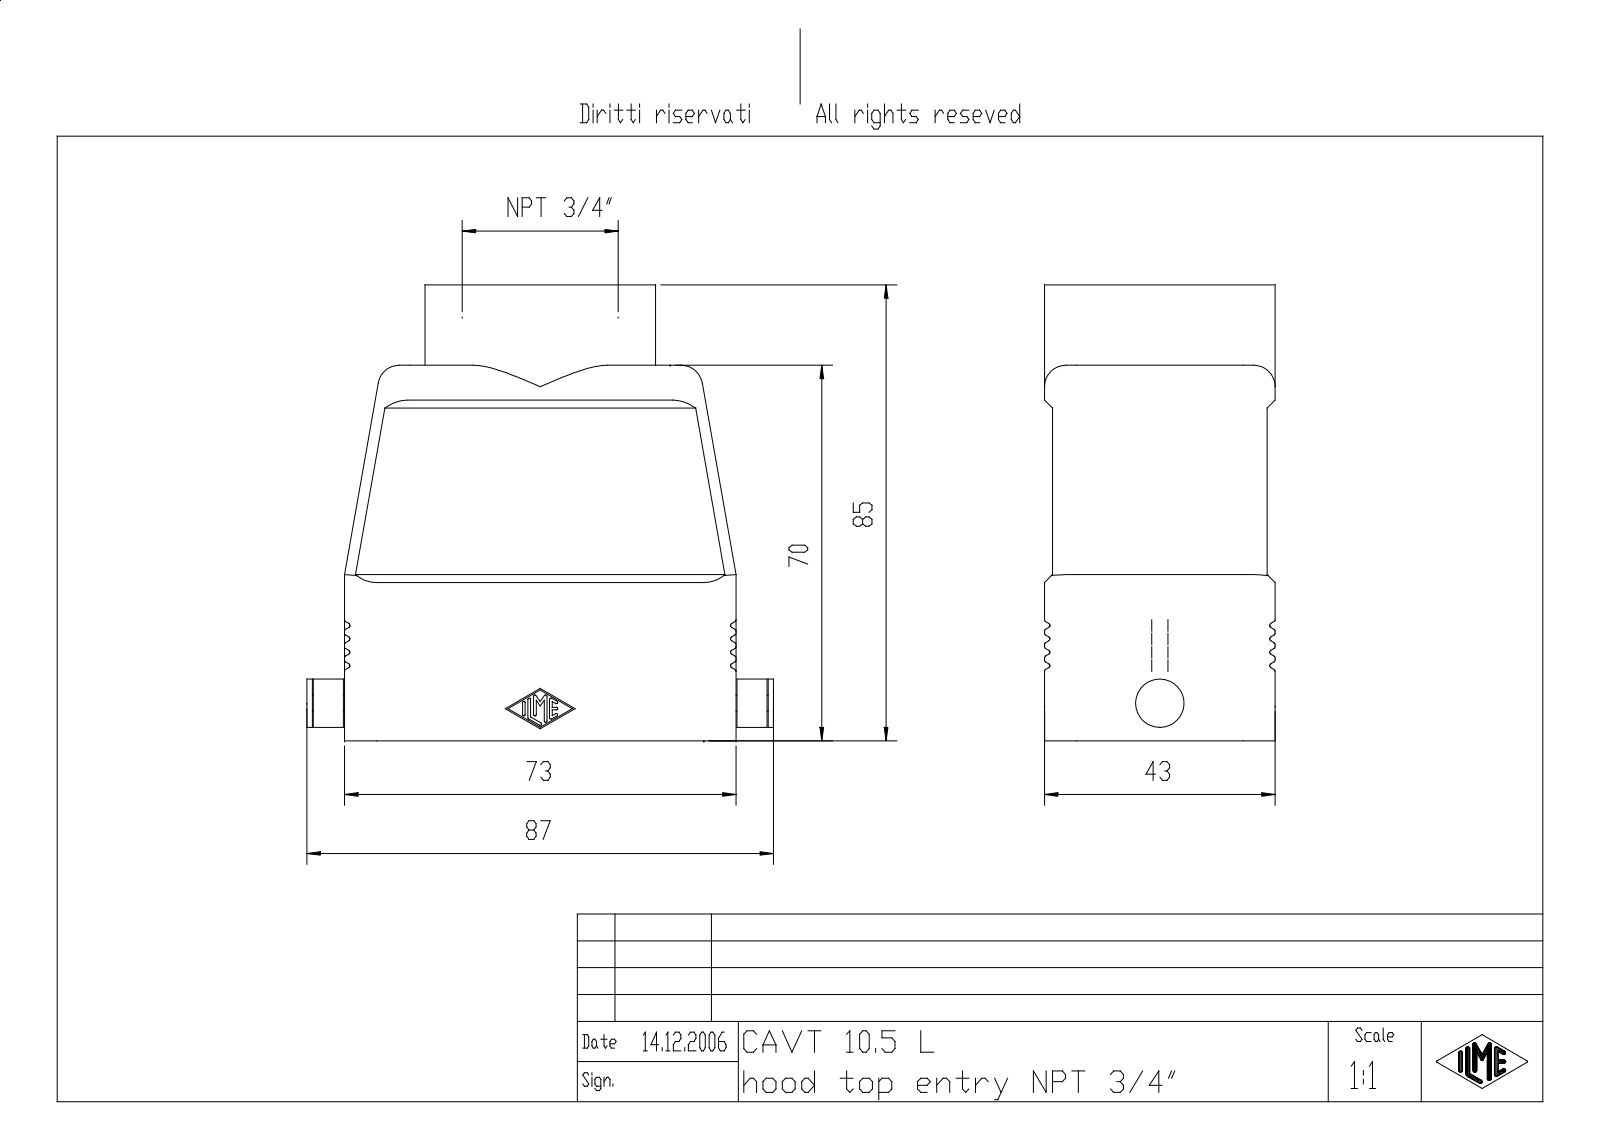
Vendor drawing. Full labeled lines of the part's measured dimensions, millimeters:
Part name (STEP PRODUCT): MSBO10755
STEP written by: Creo Elements/Direct Modeling 18.0B 02-Dec-2011 (C) Parametric Technology GmbH (AUTOMOTIVE_DESIGN)
Units: millimetres
Bodies: 1 solid, 506 faces (190 planar, 206 cylindrical, 110 other)
Overall size (bounding box): 87 × 85 × 43
Volume: 68 009 mm³ · Surface area: 41 132 mm²
Round holes (diameter × count): ⌀2.46 ×4, ⌀3.1 ×4
Round bosses / shafts (diameter × count): ⌀43 ×1, ⌀9 ×1, ⌀3 ×1
Partial cylindrical surfaces — rounded edges, fillets, slot ends (radius × count): R0.4 ×64, R0.25 ×14, R3 ×8, R6 ×8, R2 ×4, R4 ×4, R5 ×4
Main face-to-face distances: 1.5, 40, 3, 38.5, 37, 41.5, 8.5, 11.5, 70, 67
Hole centre spacings: 27, 57, 63.07
